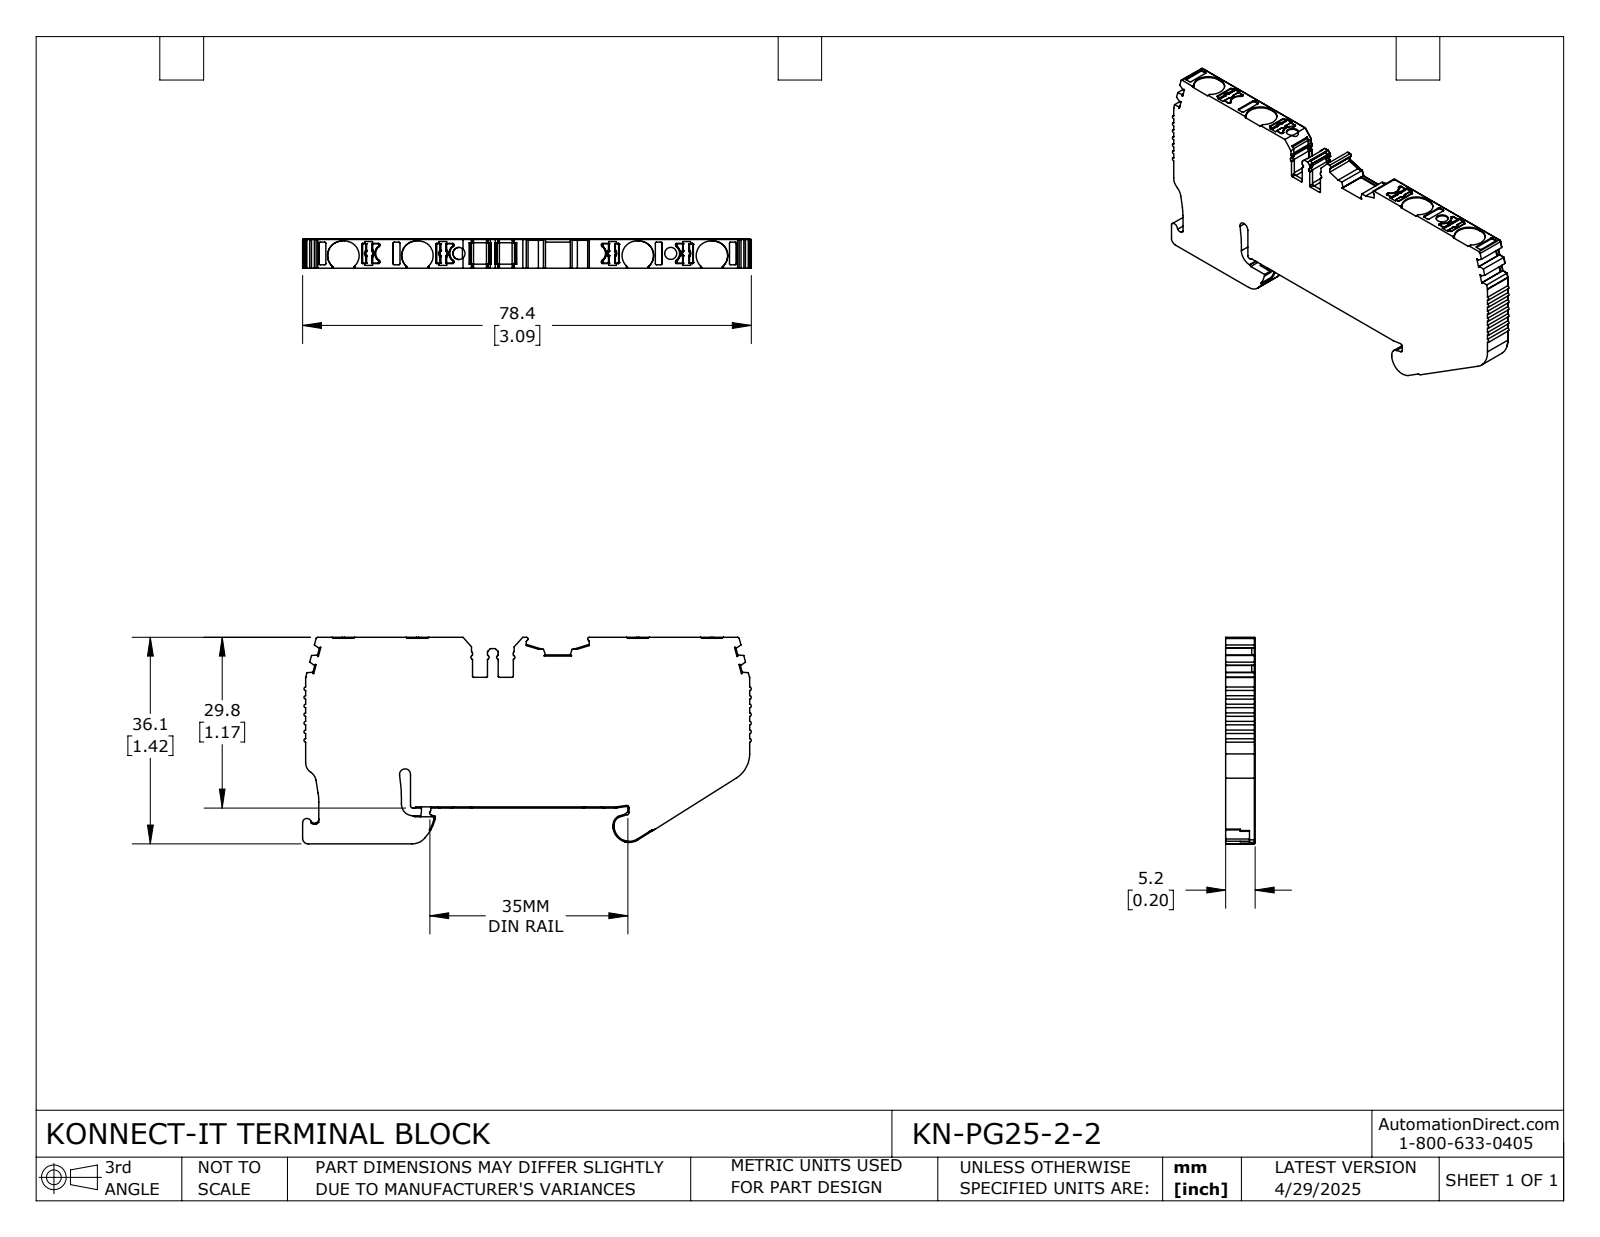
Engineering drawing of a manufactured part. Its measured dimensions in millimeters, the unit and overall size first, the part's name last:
Units: millimetres
Overall size (bounding box): 78.36 × 36.07 × 5.15
Round holes (diameter × count): ⌀2.1 ×2
Partial cylindrical surfaces — rounded edges, fillets, slot ends (radius × count): R0.2 ×77, R0.3 ×42, R0.1 ×21, R0.4 ×17, R0.15 ×16, R0.5 ×16, R1 ×8, R2.55 ×8
Main face-to-face distances: 5.15, 29.61, 29.81, 6.26, 35.87, 36.07, 6.46, 29.41, 77.52, 1.2
Hole centre spacings: 36.98
Volume: 11 929 mm³ · Surface area: 6 263 mm²
Bodies: 1 solid, 791 faces (409 planar, 313 cylindrical, 69 other)
Part name (STEP PRODUCT): KN-PG25-2-2
STEP written by: SolidWorks 2024 (CONFIG_CONTROL_DESIGN)
